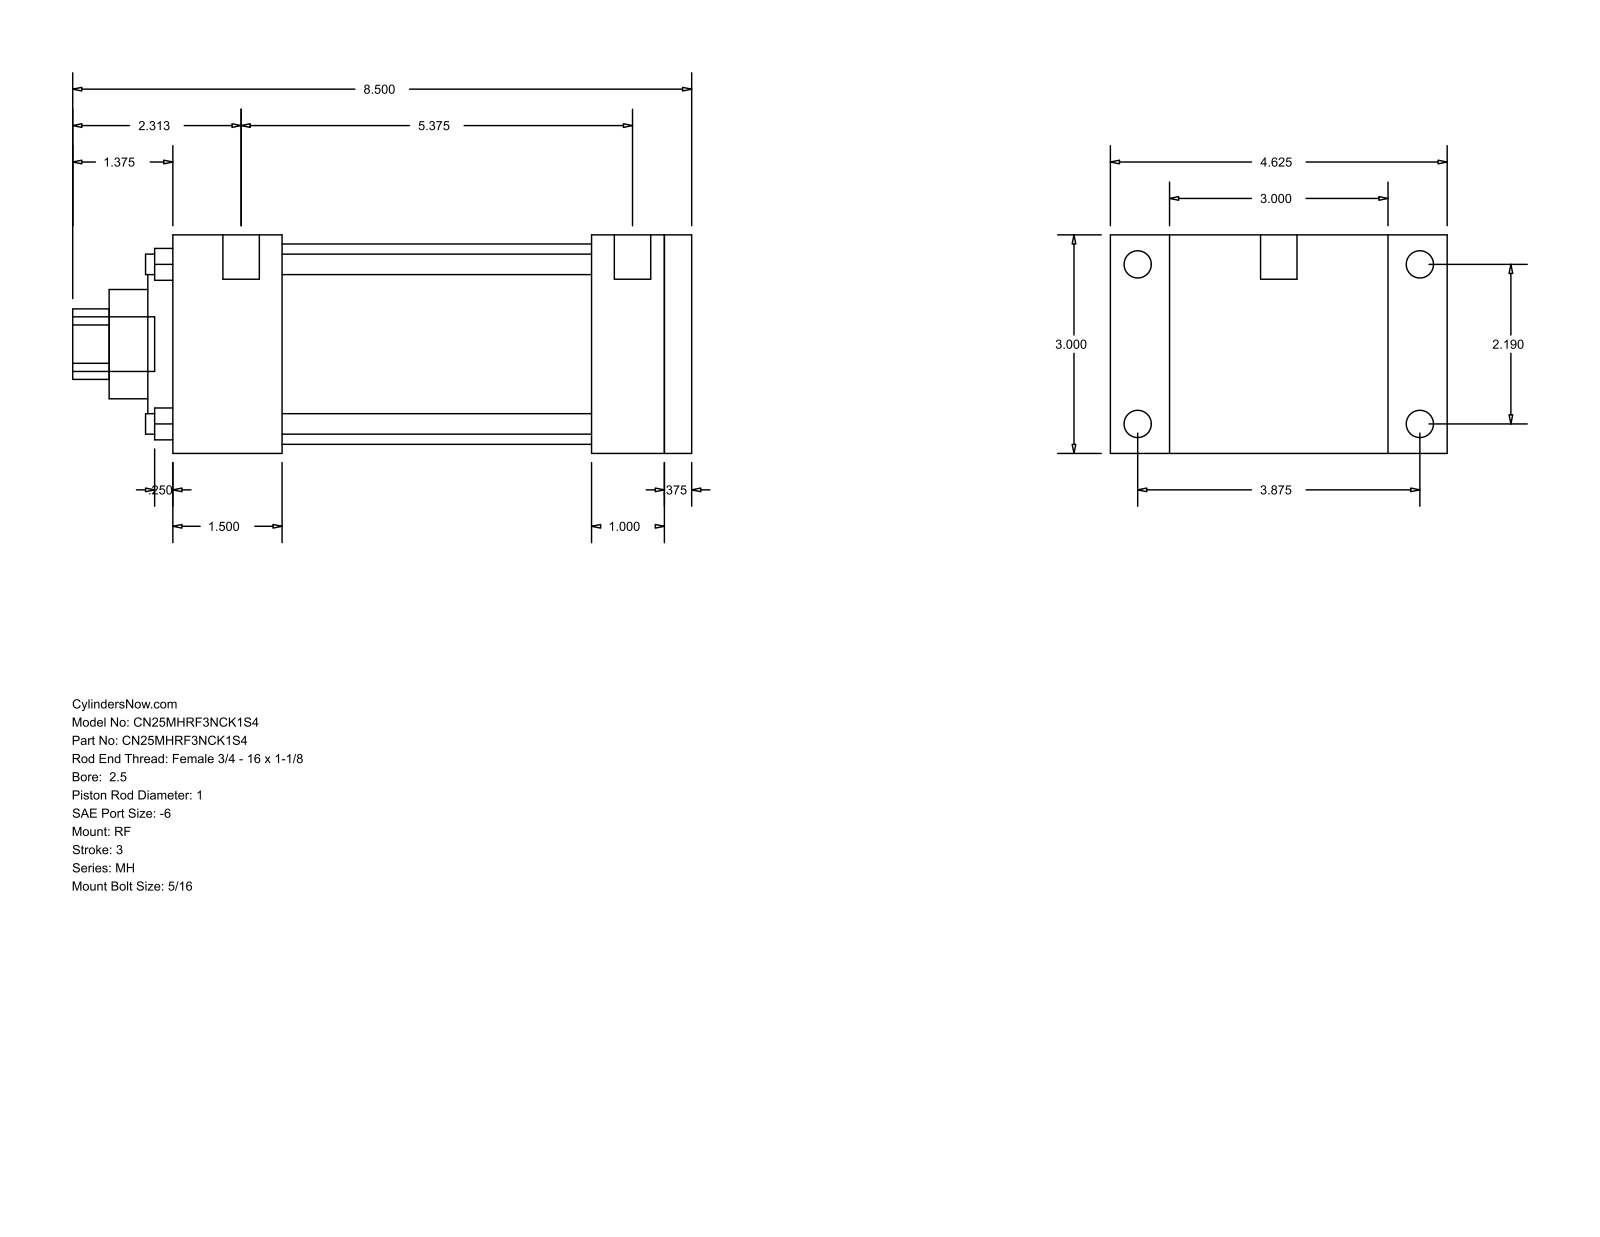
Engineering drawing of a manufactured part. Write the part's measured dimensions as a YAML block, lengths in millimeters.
part_name: "MH_RF__0250_1"
step_written_by: "GSSL Pune (CONFIG_CONTROL_DESIGN)"
units: millimeters
bodies: {solids: 0, faces: 94, planar: 65, cylindrical: 29, other: 0}
overall_size: [215.9, 117.47, 76.2]
round_holes:
  - {diameter: 7.14, count: 4}
  - {diameter: 25.4, count: 1}
  - {diameter: 38.1, count: 1}
  - {diameter: 60.33, count: 1}
  - {diameter: 69.85, count: 1}
round_bosses_or_shafts:
  - {diameter: 9.53, count: 4}
  - {diameter: 5.56, count: 4}
  - {diameter: 12.7, count: 2}
  - {diameter: 19.05, count: 1}
partial_cylinders:
  - {radius: 12.29, count: 1}
face_to_face_distances: [76.2, 9.52, 180.98, 171.46, 146.05, 25.41, 34.93, 38.11, 107.94, 133.35]
hole_center_spacings: [39.33, 55.62, 78.66]
